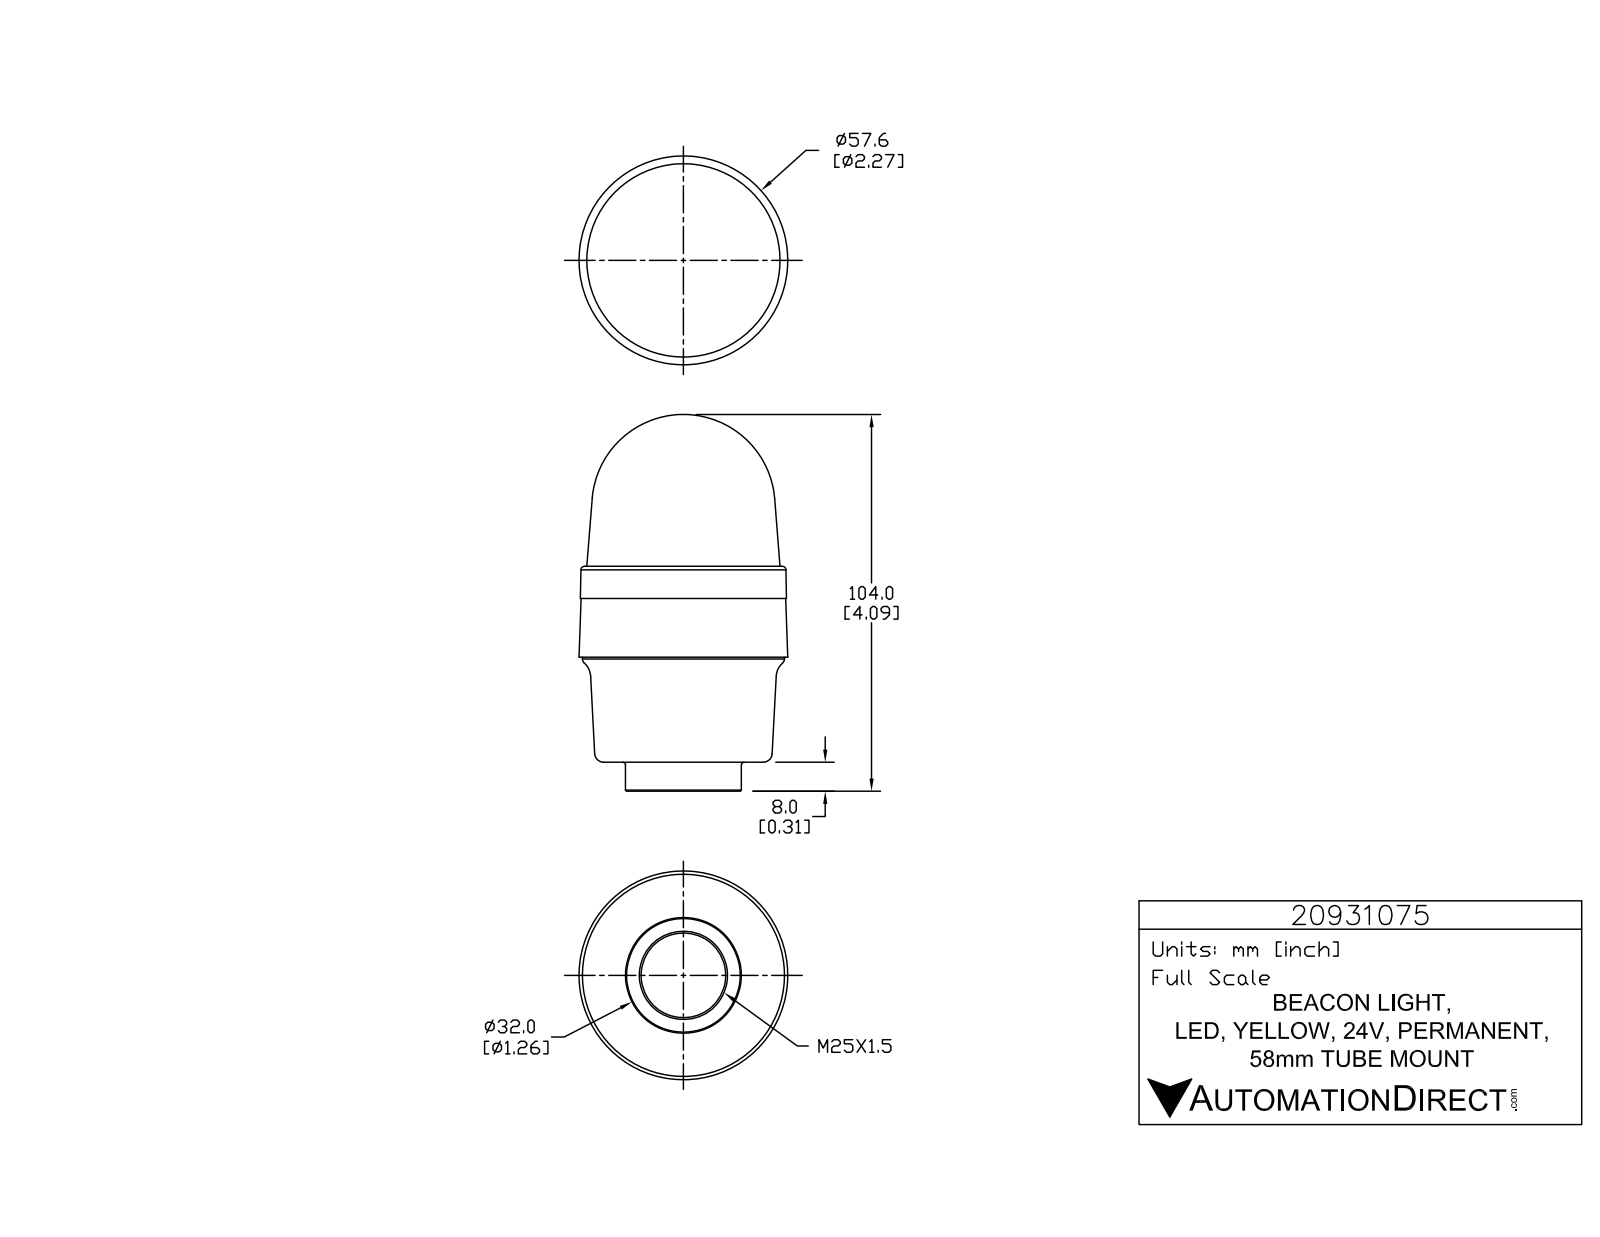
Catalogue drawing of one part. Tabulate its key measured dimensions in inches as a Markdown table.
| quantity | value |
| --- | --- |
| part name | 20931075 |
| STEP written by | SolidWorks 2017 (AUTOMOTIVE_DESIGN) |
| units | inches |
| bodies | 1 solid, 791 faces (525 planar, 168 cylindrical, 98 other) |
| overall size | 4.051 × 2.269 × 2.269 |
| volume | 11.72 in³ |
| surface area | 29.93 in² |
| round holes (diameter × count) | 0.039 × 3, 0.92 × 1 |
| round bosses / shafts (diameter × count) | 0.226 × 3, 0.056 × 3, 2.197 × 1, 1.26 × 1 |
| partial cylindrical surfaces (radius × count) | 0.008 × 6, 0.008 × 6, 0.008 × 6, 0.131 × 6, 0.004 × 3, 0.005 × 3, 0.008 × 3, 0.008 × 3 |
| main face-to-face distances | 0.315, 1.142, 1.457, 0.988, 2.13, 2.445, 0.35, 0.638, 1.78, 2.094 |
